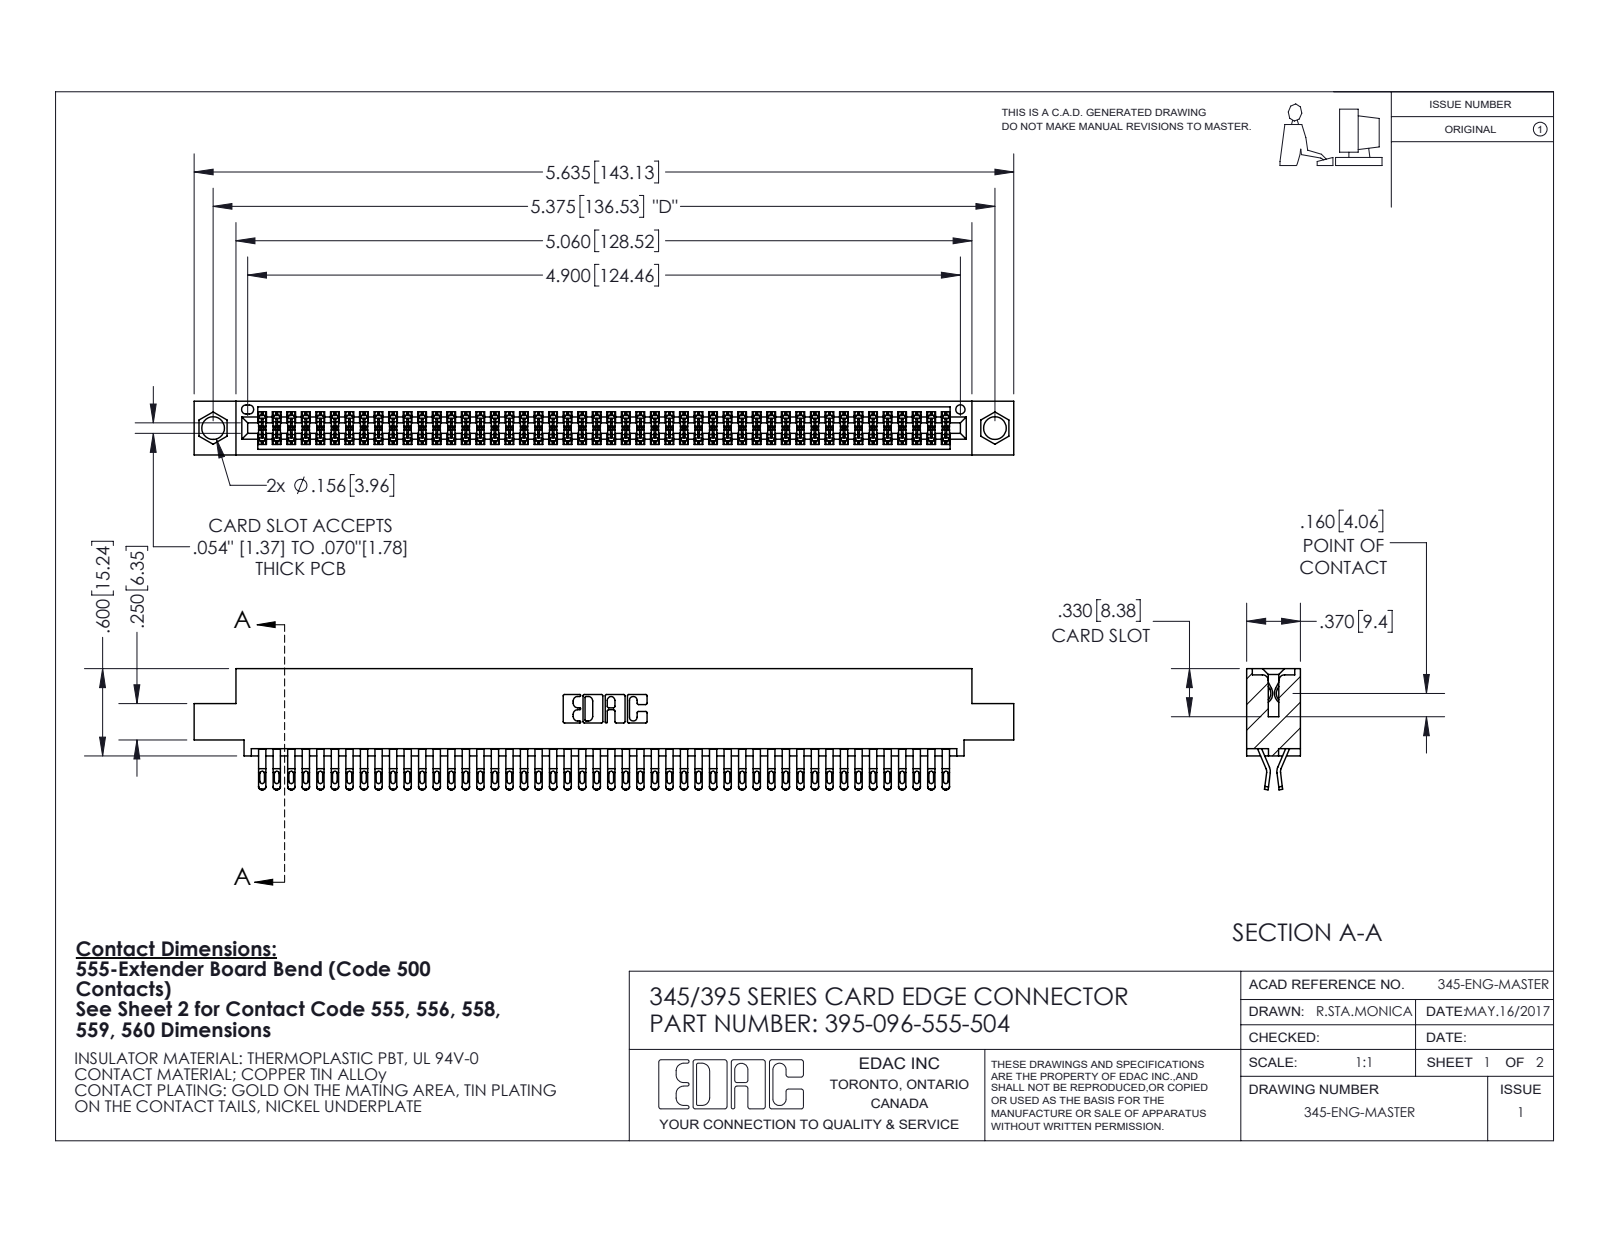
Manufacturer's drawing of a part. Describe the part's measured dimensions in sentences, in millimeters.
The part is named "395-096-555-504; 345 Part_0.110 Offset - 0.156 Dia-TI; 345-292-001_555 Tail". Its 3-D file was written by "SolidWorks 2020 (CONFIG_CONTROL_DESIGN)". It is 97 solids with 5520 faces: 3074 planar, 2446 cylindrical and 0 other. Overall it measures 143.1 by 21.1 by 9.4 millimeters. Its volume is 14 100 cubic millimeters and its surface area 21 810 square millimeters. Round holes: 2 of diameter 4, 1 of diameter 1.6. Partial cylindrical surfaces (rounded edges, fillets, slot ends): 240 of radius 0.4, 192 of radius 0.2, 192 of radius 0.5, 22 of radius 0.3, 6 of radius 0.2, 6 of radius 0.8, 3 of radius 0.7, 2 of radius 0.3. The main face-to-face distances are 7.6, 1.8, 0.6, 9.4, 5.1, 2.5, 6.9, 5.7, 4.4, 3.8. The hole center spacings are 6.9, 130.5, 136.5.
